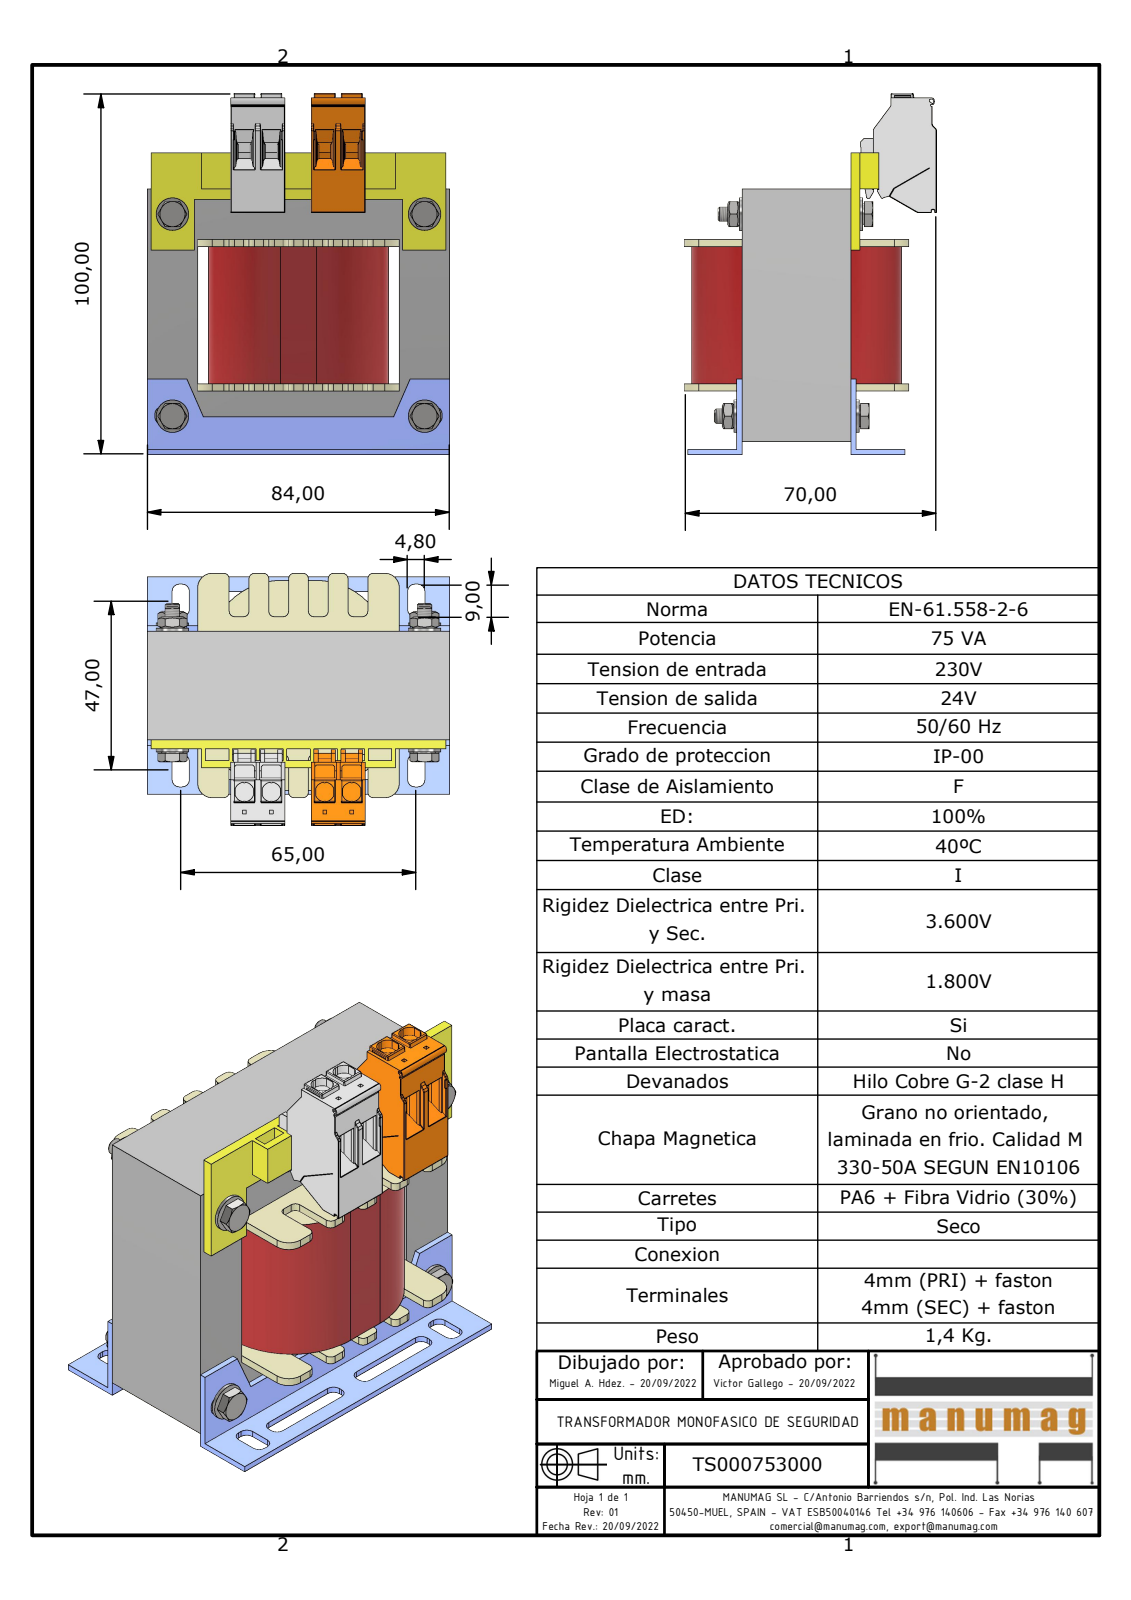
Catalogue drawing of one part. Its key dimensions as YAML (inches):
part_name: "TS000753000; EI84 x 70 - 30 (RC28); AF28DIN; EI 84 X 70 - 30 (+6 more)"
step_written_by: "Autodesk Inventor 2023 (AUTOMOTIVE_DESIGN)"
units: inches
bodies: {solids: 23, faces: 3769, planar: 3015, cylindrical: 520, other: 234}
overall_size: [3.945, 3.307, 2.744]
volume: 14.38
surface_area: 118.2
round_holes:
  - {diameter: 0.128, count: 4}
  - {diameter: 0.169, count: 4}
  - {diameter: 0.177, count: 4}
  - {diameter: 0.157, count: 2}
round_bosses_or_shafts:
  - {diameter: 0.354, count: 4}
  - {diameter: 0.232, count: 4}
  - {diameter: 0.143, count: 4}
  - {diameter: 0.157, count: 2}
partial_cylinders:
  - {radius: 0.006, count: 160}
  - {radius: 0.008, count: 48}
  - {radius: 0.079, count: 40}
  - {radius: 0.059, count: 32}
  - {radius: 0.02, count: 12}
  - {radius: 0.012, count: 7}
  - {radius: 0.039, count: 4}
  - {radius: 0.106, count: 4}
face_to_face_distances: [0.551, 2.205, 1.102, 1.181, 1.654, 2.756, 0.059, 0.079, 0.63, 2.126]
hole_center_spacings: [2.205, 2.756, 3.529]
